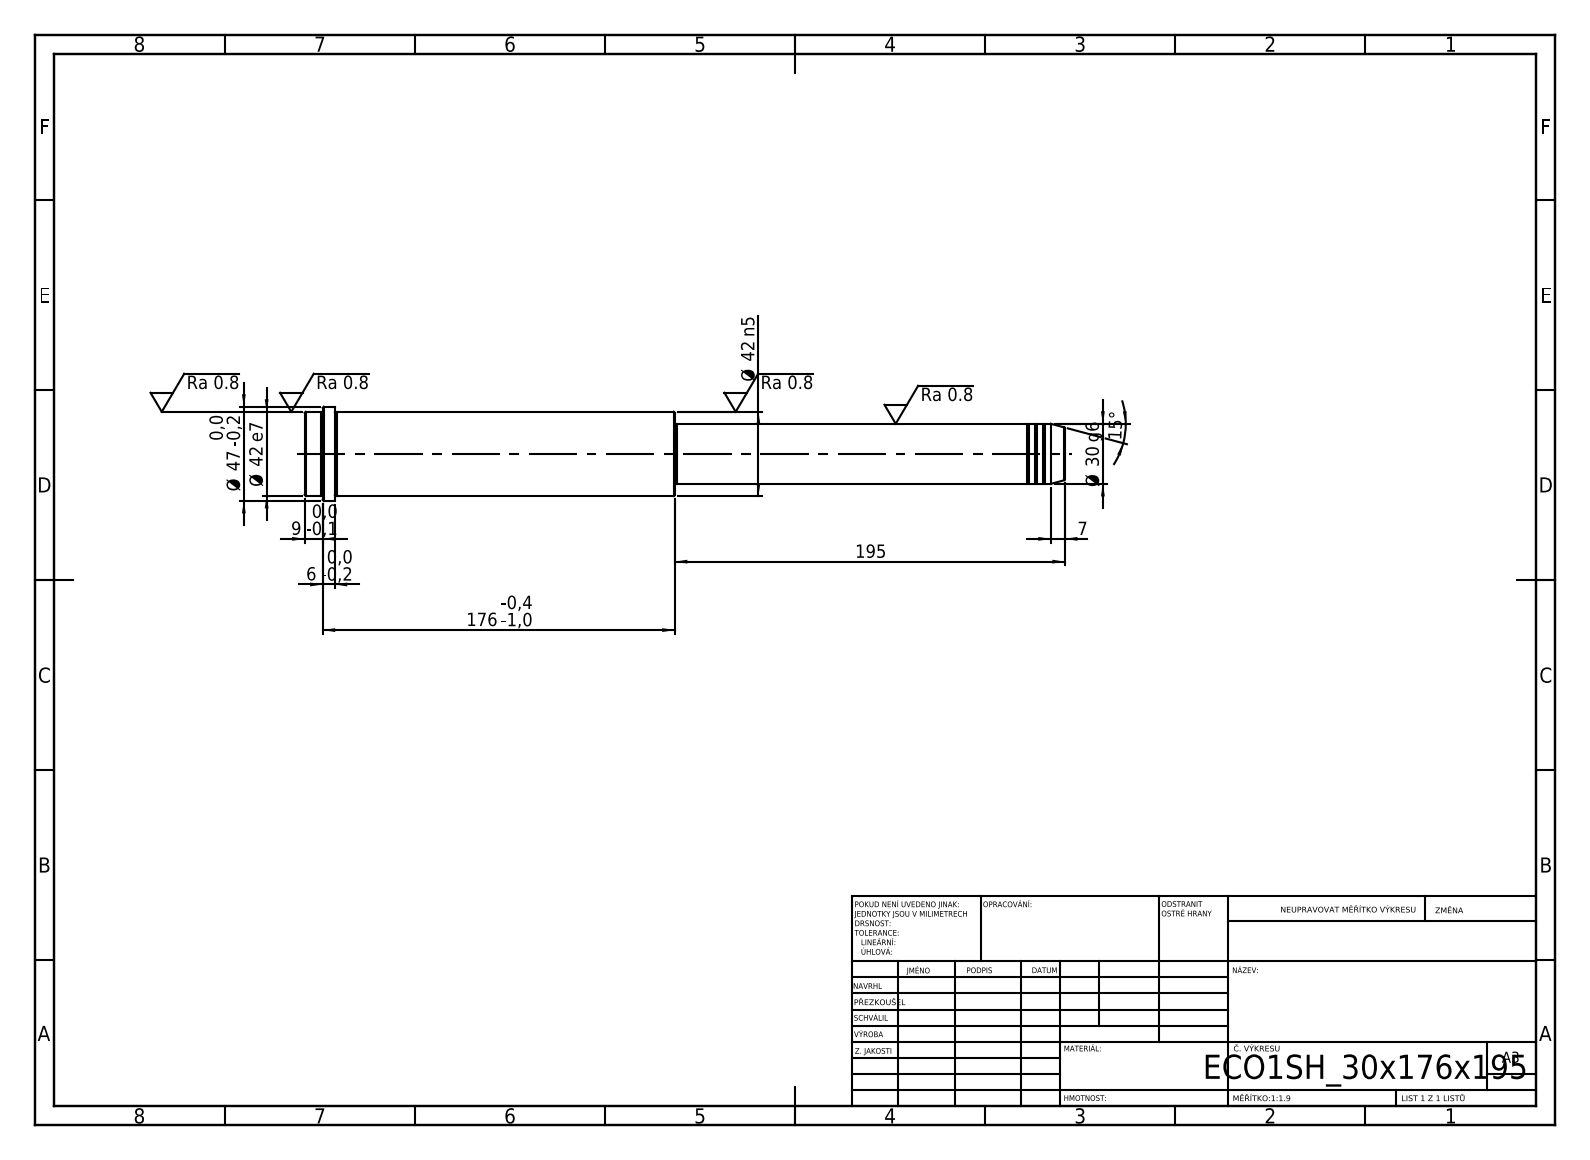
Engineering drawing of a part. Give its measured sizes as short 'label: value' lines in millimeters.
written by: SolidWorks 2019 (CONFIG_CONTROL_DESIGN)
unit: mm
bodies: 1 solid, 52 faces (6 planar, 16 cylindrical, 30 other)
size: 380 × 47 × 47
volume: 395 337 mm³; area: 46 422 mm²
bosses: 1× ⌀47, 1× ⌀42, 1× ⌀30, 1× ⌀29
face distances: 185, 195, 380, 365, 170, 15, 371, 176, 6, 9
